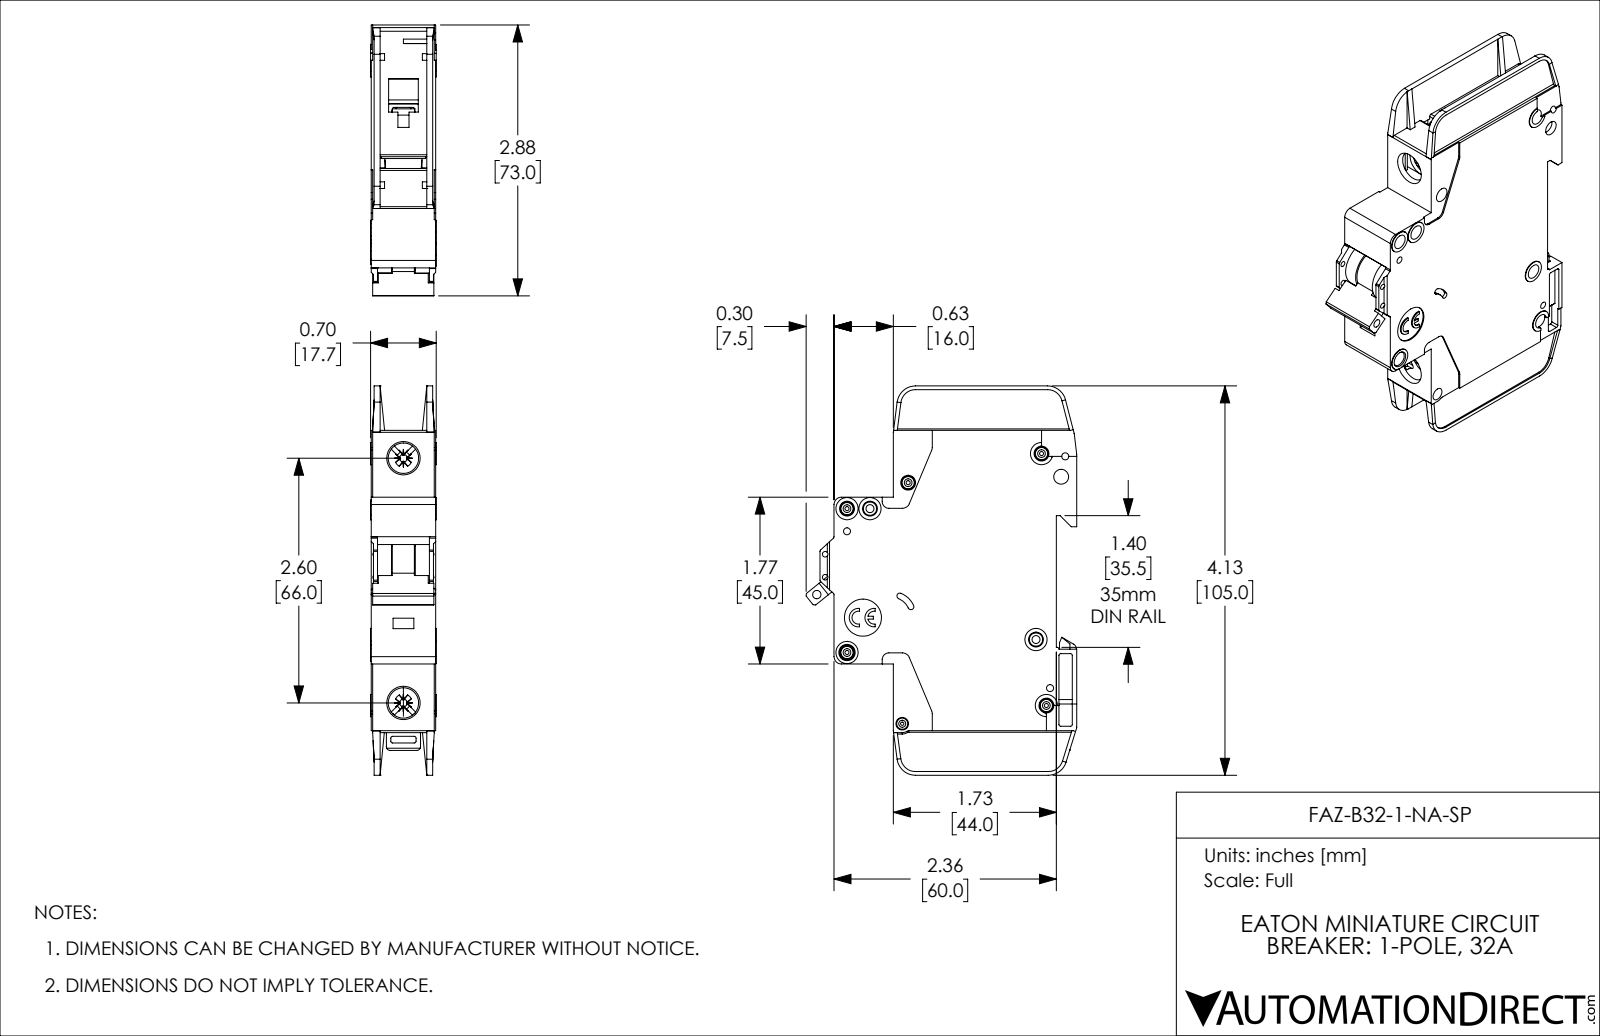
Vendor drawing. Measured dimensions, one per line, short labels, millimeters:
name: FAZ-B32-1-NA-SP
written by: SolidWorks 2019 (AUTOMOTIVE_DESIGN)
unit: mm
bodies: 1 solid, 1127 faces (671 planar, 357 cylindrical, 99 other)
size: 105 × 73.1 × 17.7
volume: 76 720 mm³; area: 26 460 mm²
holes: 8× ⌀4, 5× ⌀1.1, 4× ⌀1.9, 2× ⌀1.5, 2× ⌀2.2, 2× ⌀8.2, 1× ⌀0.9, 1× ⌀2.3, 1× ⌀2.5, 1× ⌀3.4, 1× ⌀10
bosses: 5× ⌀3.3, 4× ⌀6, 2× ⌀3, 1× ⌀2.5
rounds: 42× R0.5, 10× R0.4, 10× R1, 8× R2, 5× R5, 4× R0.2, 4× R0.7, 4× R1.1
face distances: 1.2, 17.4, 15, 16.2, 2.4, 13.8, 0.4, 0.8, 12.6, 14.6
hole spacings: 6.2, 13.6, 22.1, 4.8, 5.1, 5.2, 5.6, 6.1
